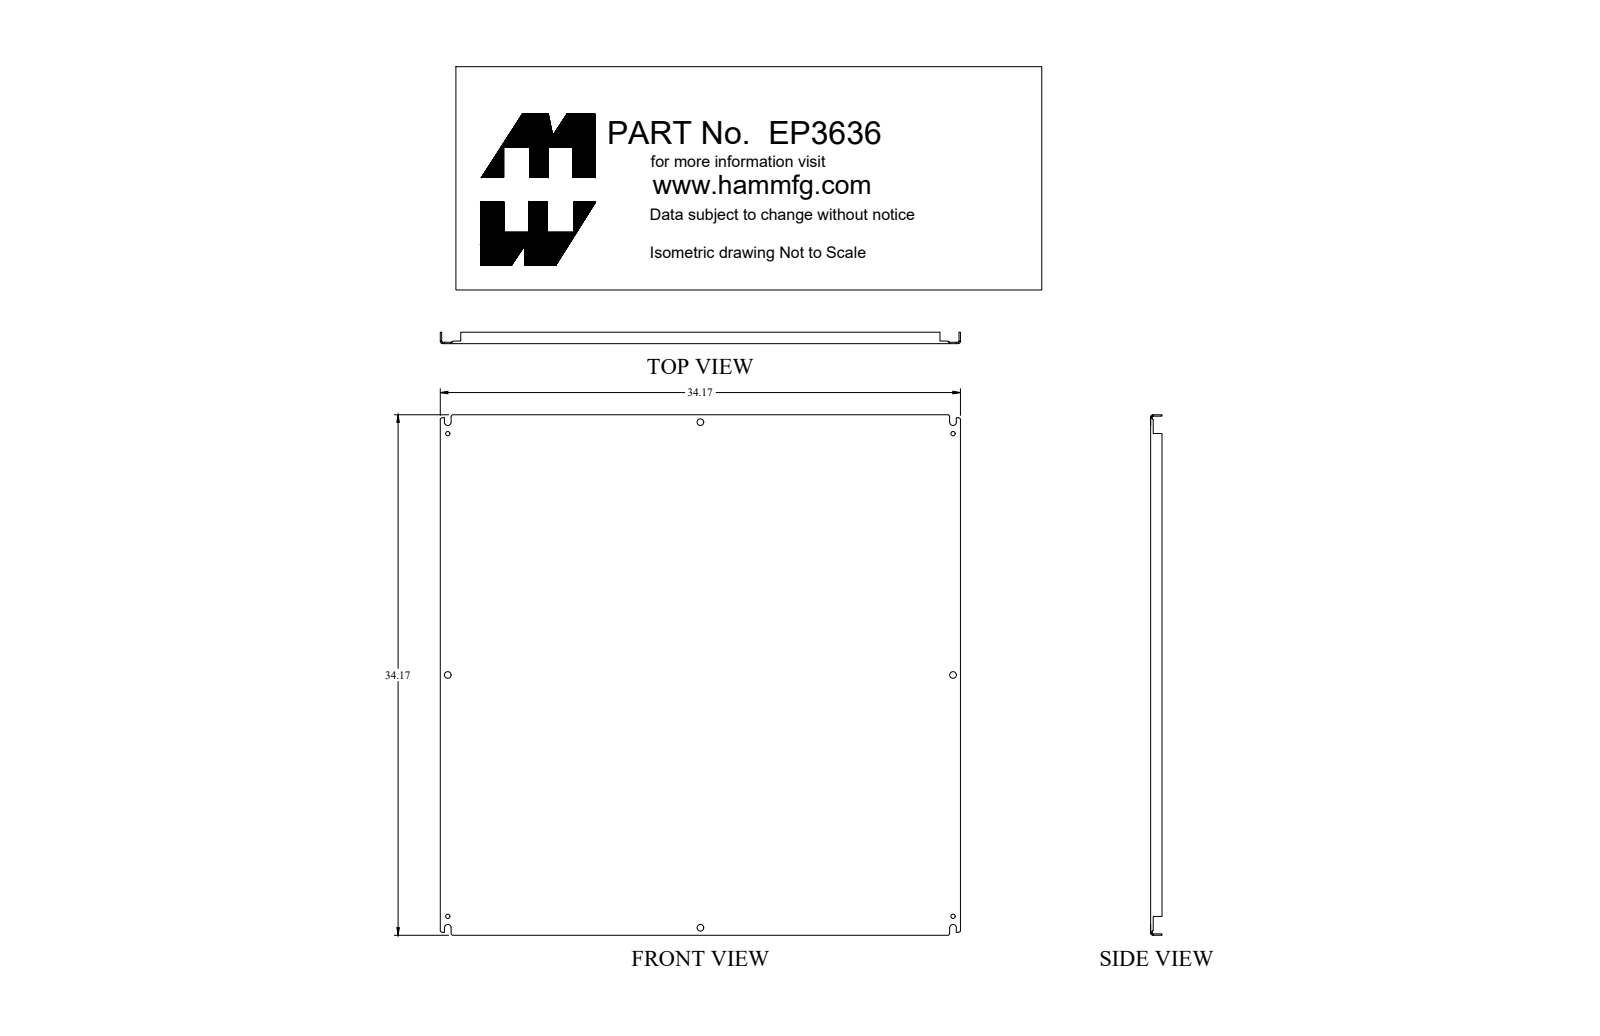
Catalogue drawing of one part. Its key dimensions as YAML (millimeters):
part_name: "EP3636"
step_written_by: "SolidWorks 2018 (AUTOMOTIVE_DESIGN)"
units: millimeters
bodies: {solids: 1, faces: 136, planar: 74, cylindrical: 46, other: 16}
overall_size: [867.9, 867.9, 19.1]
volume: 1935000
surface_area: 1614000
round_holes:
  - {diameter: 7.1, count: 4}
  - {diameter: 11.1, count: 4}
partial_cylinders:
  - {radius: 1.2, count: 4}
  - {radius: 1.6, count: 4}
  - {radius: 3.6, count: 4}
  - {radius: 5.6, count: 4}
face_to_face_distances: [2.4, 865.5, 867.9, 863.1, 19.1, 16.6, 4.3, 1.9, 14.7, 31.4]
hole_center_spacings: [402.4, 421.9, 596.1, 843, 925.5, 934.1, 804.9, 1165.5]
